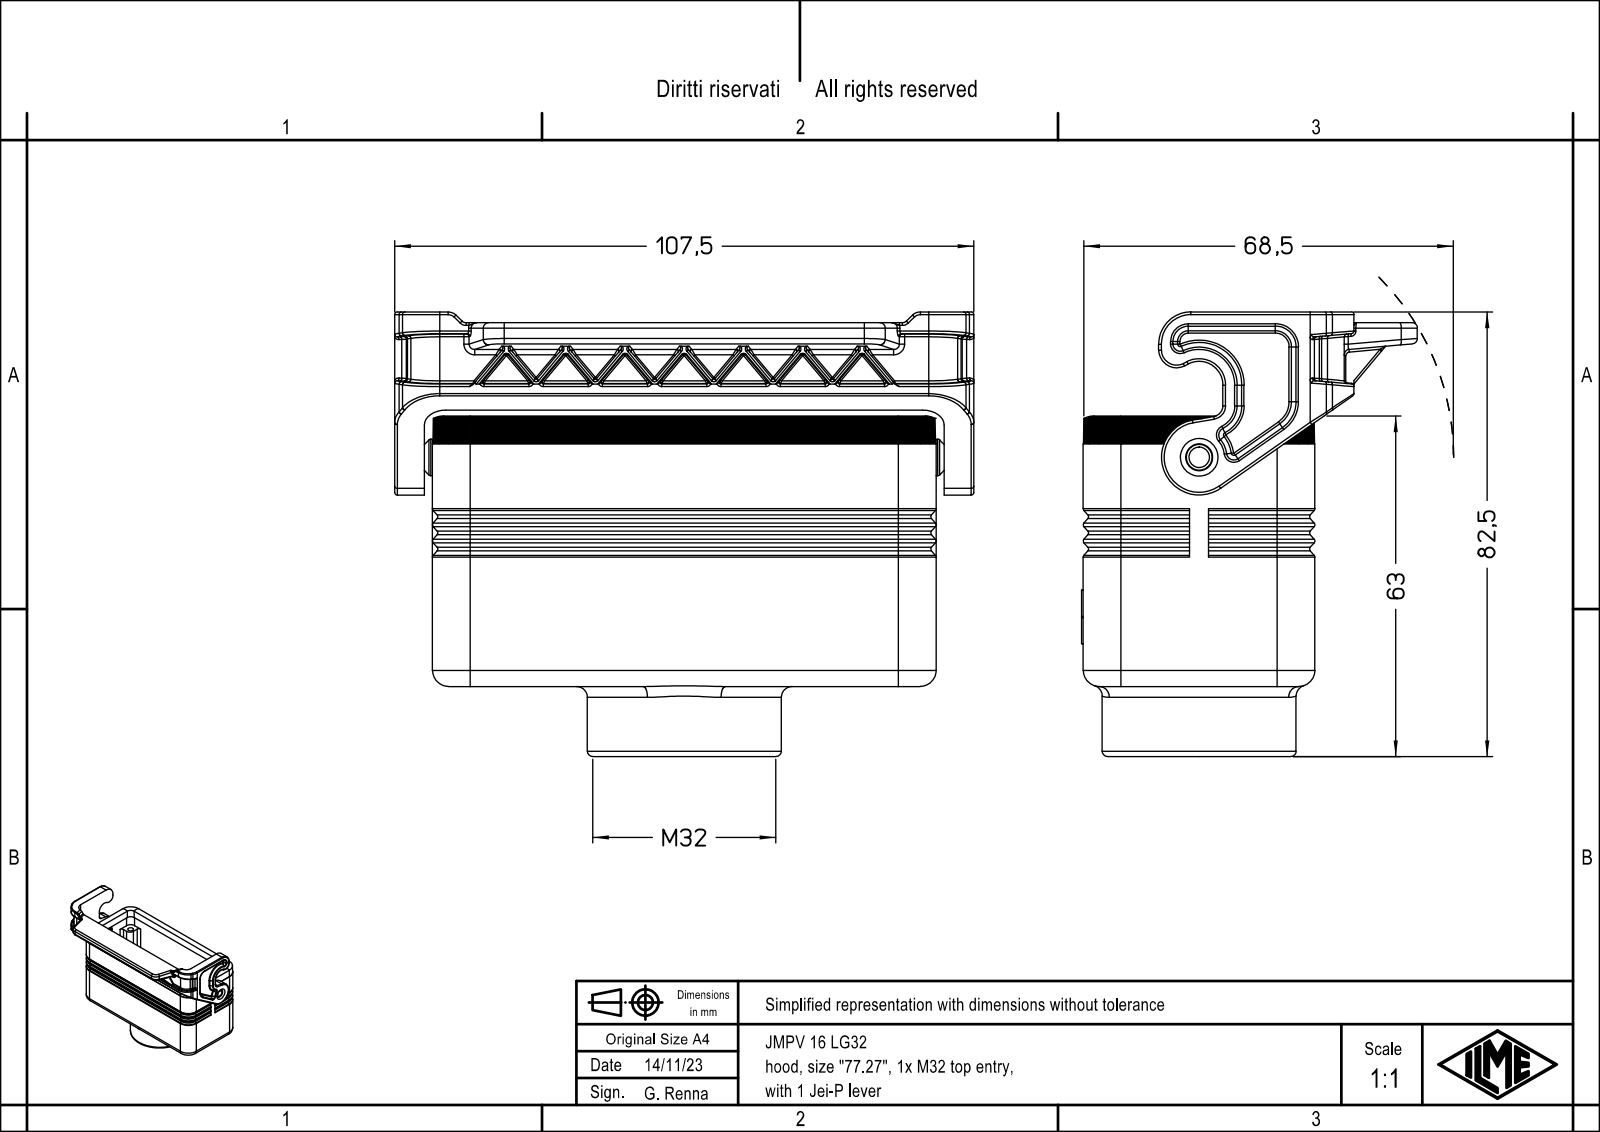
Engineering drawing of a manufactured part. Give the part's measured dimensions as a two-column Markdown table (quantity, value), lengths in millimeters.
| quantity | value |
| --- | --- |
| part name | JMPV 16 LG32 |
| STEP written by | Creo Elements/Direct Modeling 20.1B 02-Apr-2019 (C) Parametric Technology GmbH (AUTOMOTIVE_DESIGN) |
| units | millimeters |
| bodies | 1 solid, 999 faces (246 planar, 395 cylindrical, 358 other) |
| overall size | 107.5 × 82.5 × 62.3 |
| volume | 77 606 mm³ |
| surface area | 45 716 mm² |
| round holes (diameter × count) | 3 × 4, 3.5 × 4, 4.8 × 1, 28 × 1, 30.6 × 1 |
| round bosses / shafts (diameter × count) | 36 × 1, 6.8 × 1 |
| partial cylindrical surfaces (radius × count) | 0.5 × 105, 0.3 × 99, 1.5 × 22, 0.33 × 15, 3 × 12, 1 × 11, 7 × 9, 4 × 8 |
| main face-to-face distances | 3.5, 39.5, 36, 43, 2.8, 95, 5, 3.25, 6.75, 42.75 |
| hole center spacings | 41.03, 27, 77.5, 82.07 |
